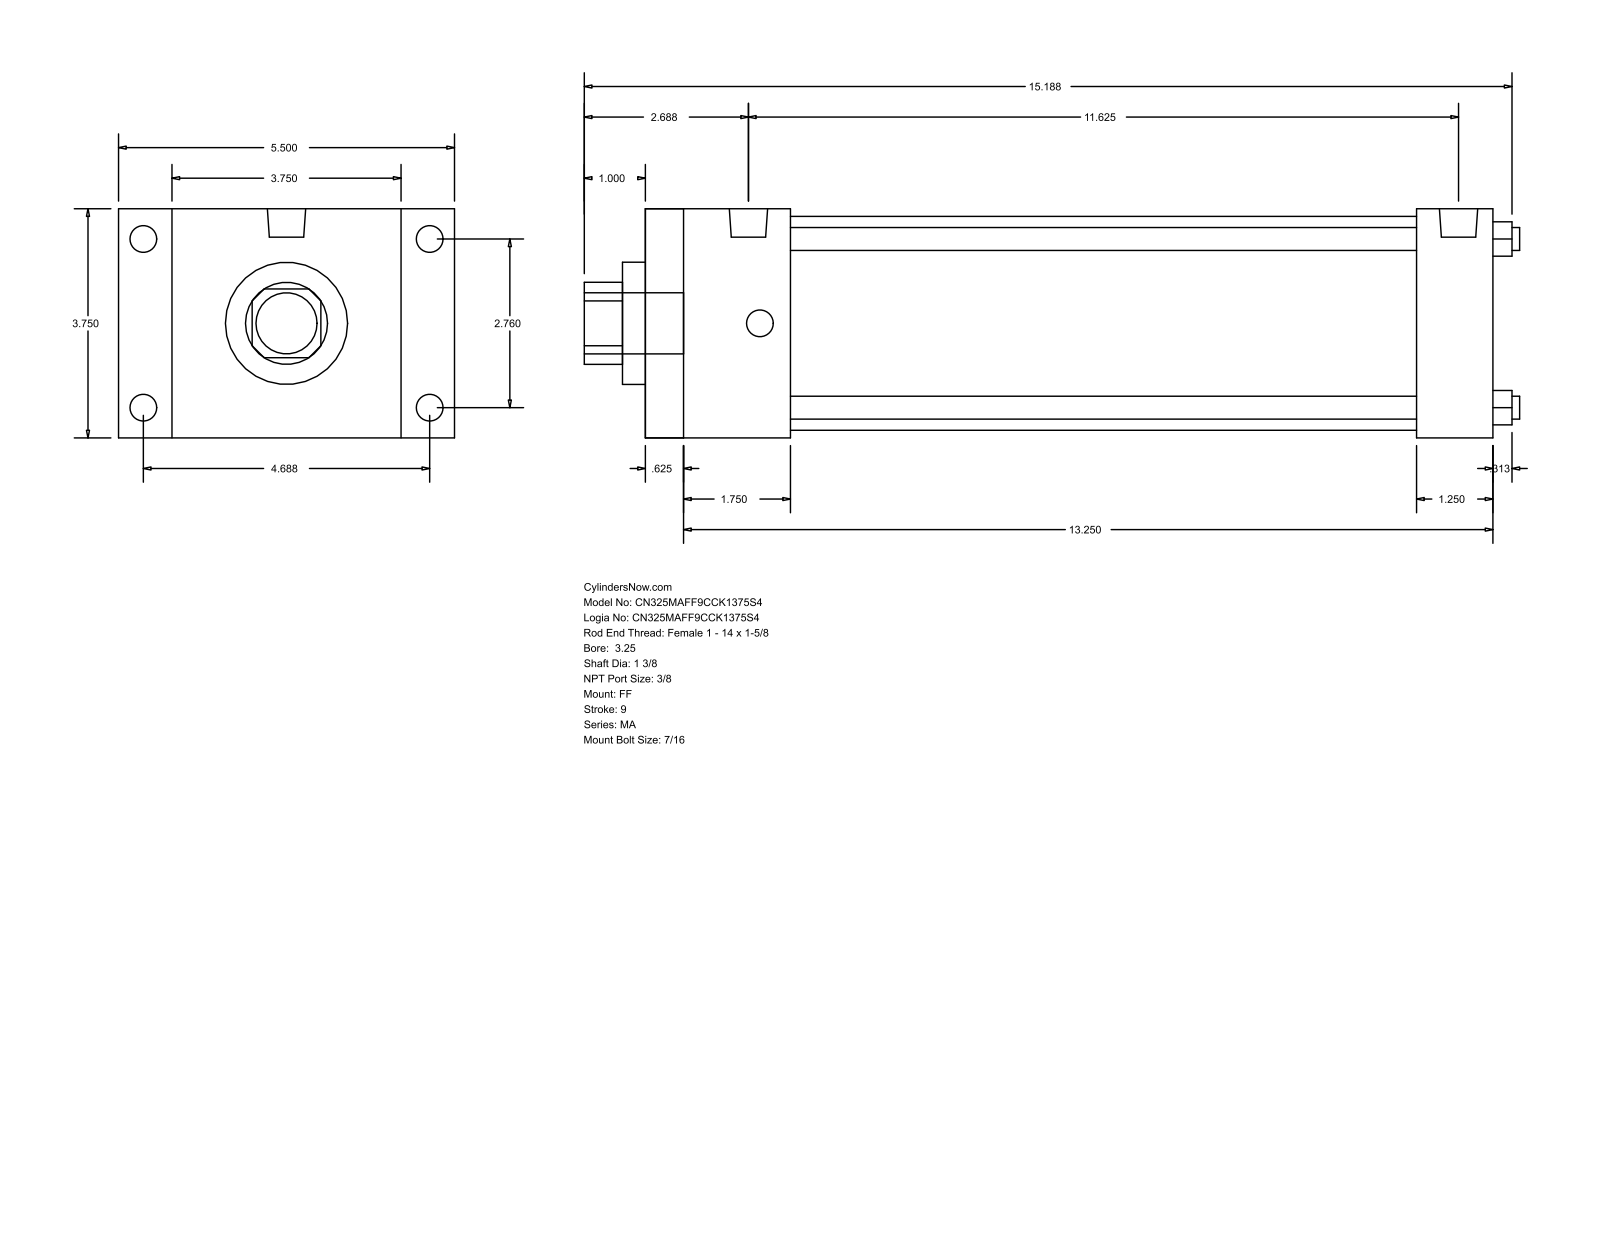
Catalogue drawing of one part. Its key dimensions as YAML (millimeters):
part_name: "MA_FF__0325_1.375"
step_written_by: "GSSL Pune (CONFIG_CONTROL_DESIGN)"
units: millimeters
bodies: {solids: 0, faces: 92, planar: 64, cylindrical: 28, other: 0}
overall_size: [388.94, 139.7, 95.25]
round_holes:
  - {diameter: 9.53, count: 4}
  - {diameter: 34.92, count: 1}
  - {diameter: 50.8, count: 1}
  - {diameter: 88.9, count: 1}
round_bosses_or_shafts:
  - {diameter: 11.11, count: 8}
  - {diameter: 15.93, count: 2}
  - {diameter: 25.4, count: 1}
partial_cylinders:
  - {radius: 17.06, count: 1}
face_to_face_distances: [95.24, 352.42, 15.87, 336.55, 22.23, 117.47, 60.32, 320.67, 44.45, 304.8]
hole_center_spacings: [49.57, 70.1, 99.14]
